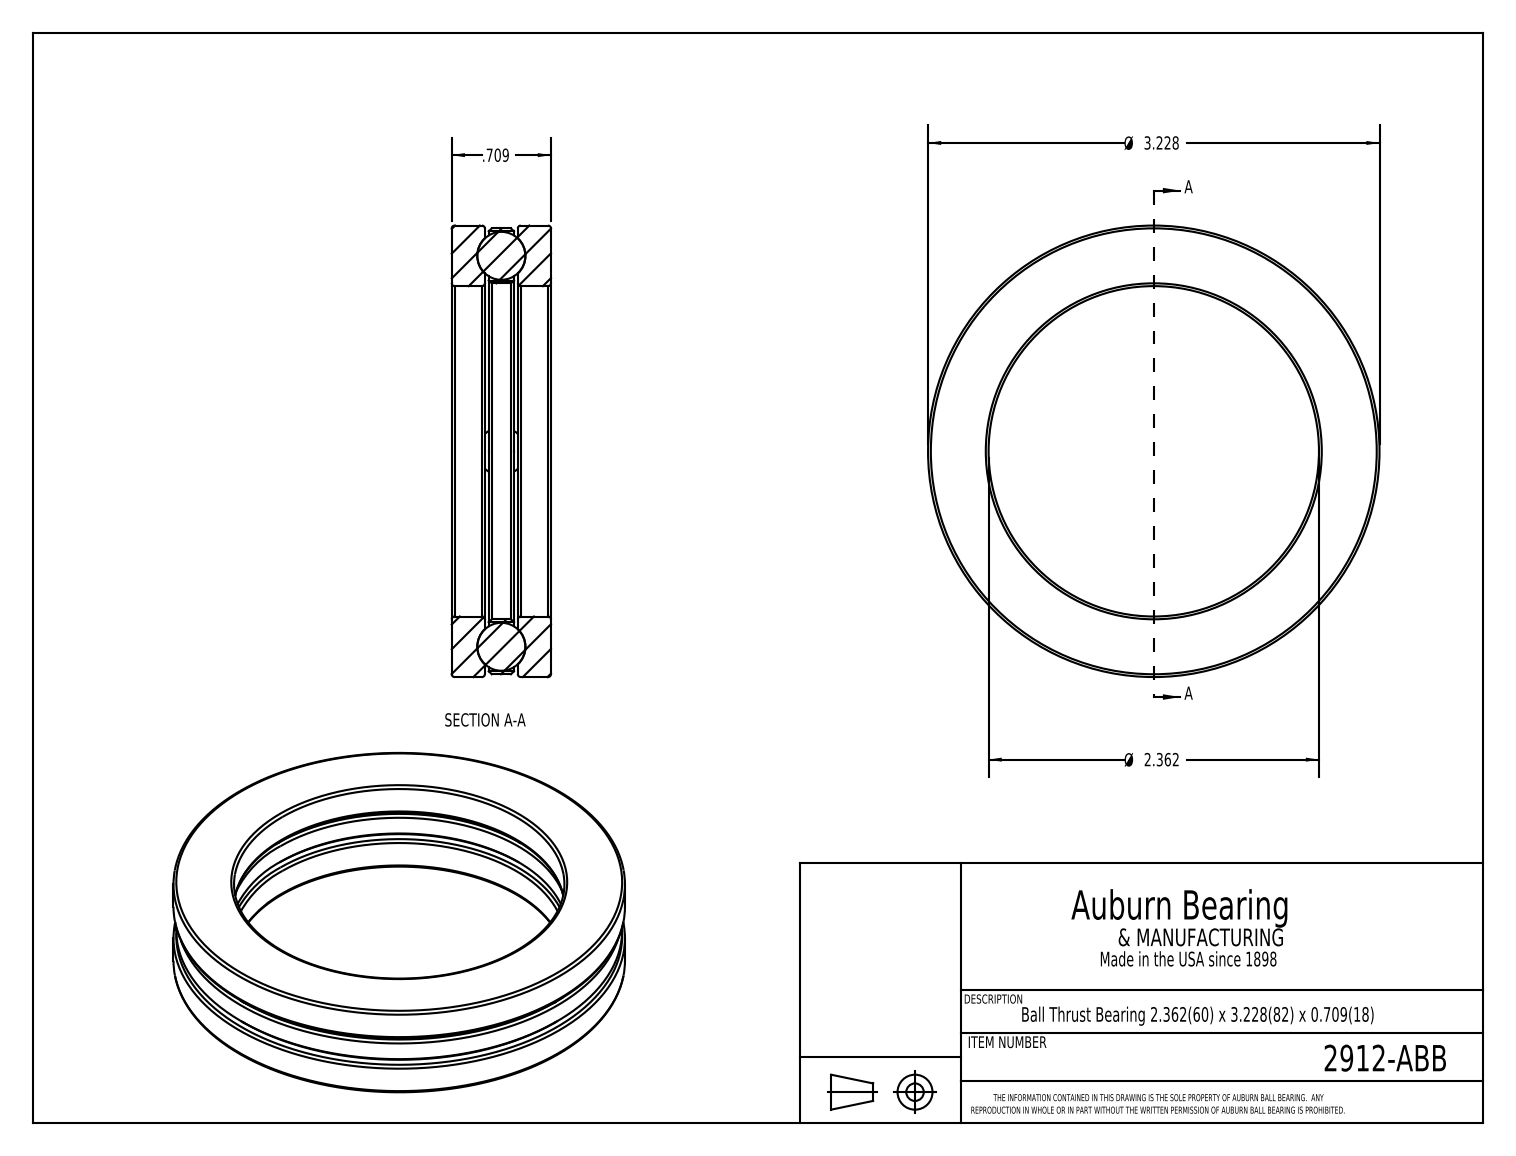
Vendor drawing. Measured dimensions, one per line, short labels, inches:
name: 2912-ABB
written by: SolidWorks 2017 (CONFIG_CONTROL_DESIGN)
unit: in
bodies: 7 solids, 42 faces (14 planar, 10 cylindrical, 18 other)
size: 3.228 × 3.228 × 0.709
volume: 2.25 in³; area: 34.51 in²
holes: 4× ⌀0.353, 1× ⌀2.362, 1× ⌀2.402
bosses: 1× ⌀3.228, 1× ⌀3.188
face distances: 0.266, 0.443, 0.236, 0.709, 0.177, 0.472, 0.03, 0.207
hole spacings: 1.398, 1.976, 2.795
